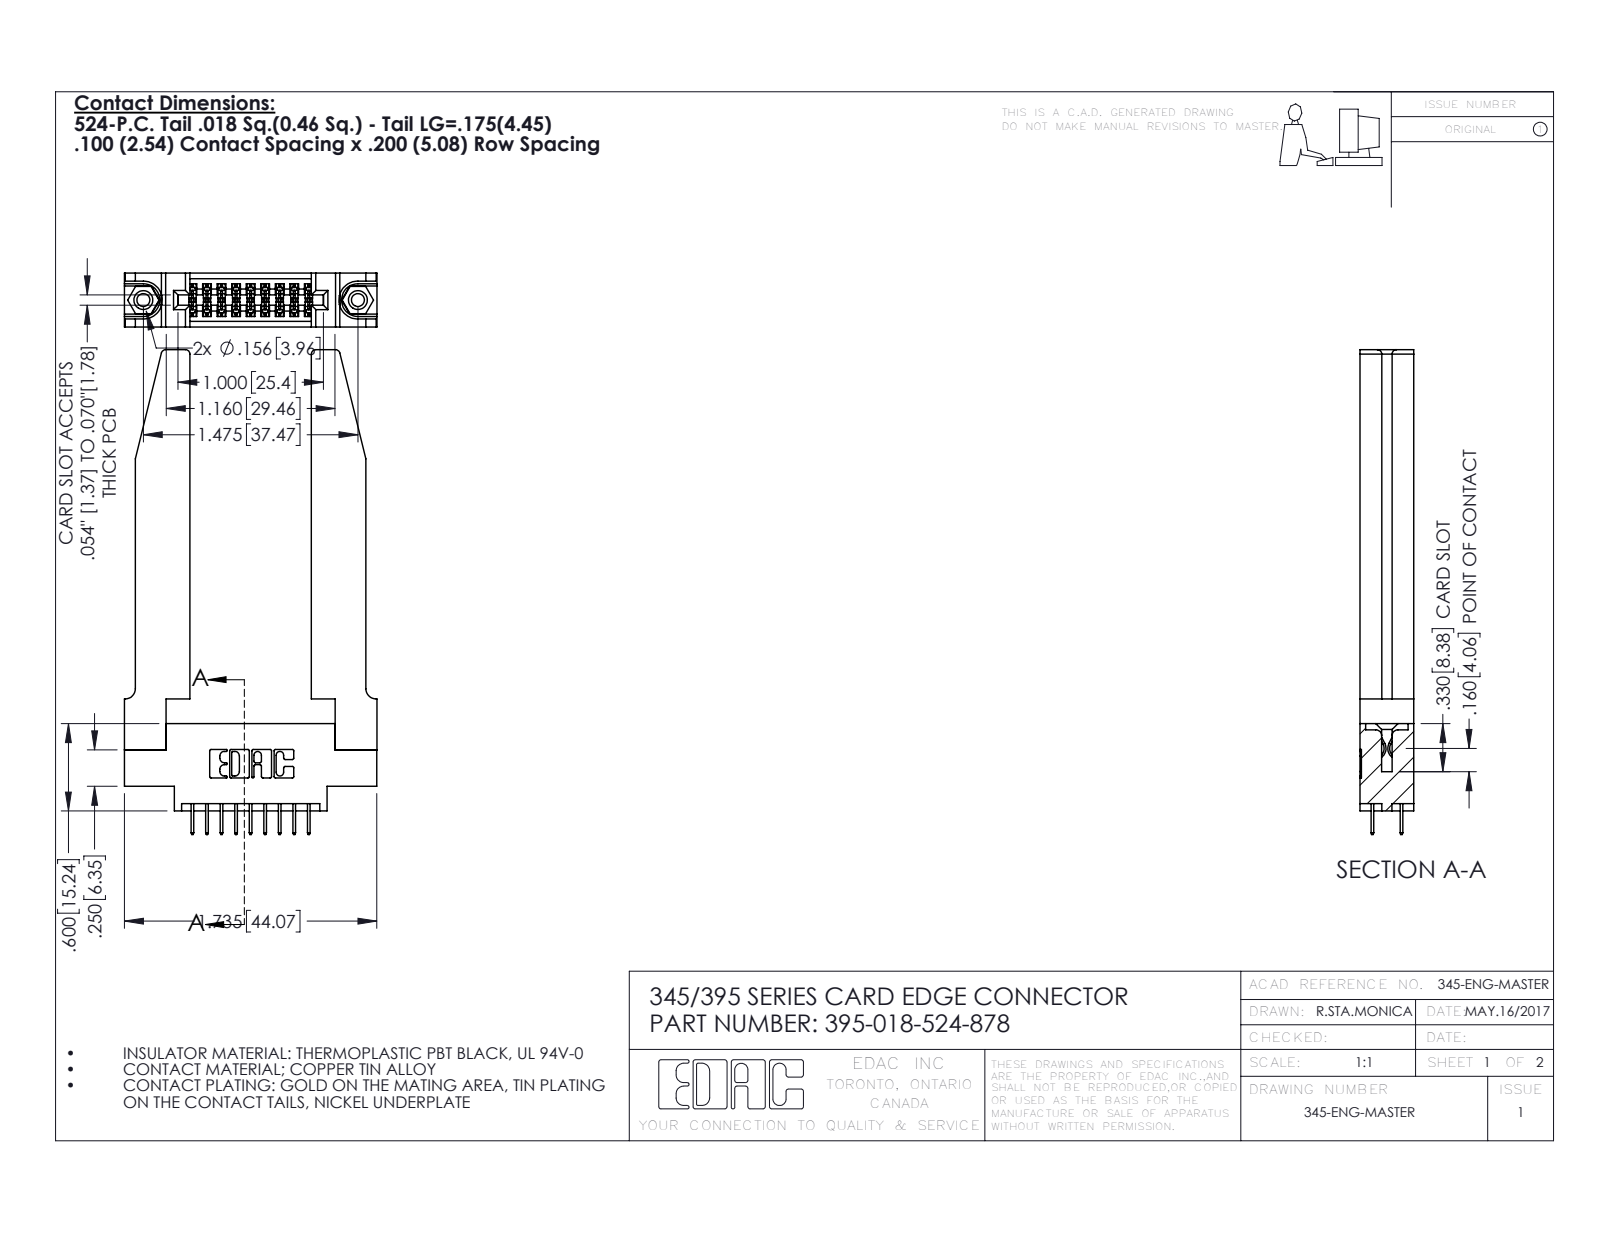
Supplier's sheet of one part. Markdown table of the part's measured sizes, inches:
| quantity | value |
| --- | --- |
| part name | 345-220-078_345-220-078; 345 Part_0.170 Offset - 0.156 Dia-TH; 345-250-001_345-250-001-102; 345-292-001_345-293-124 (+1 more) |
| STEP written by | SolidWorks 2016 (CONFIG_CONTROL_DESIGN) |
| units | inches |
| bodies | 23 solids, 1336 faces (928 planar, 356 cylindrical, 52 other) |
| overall size | 3.332 × 1.736 × 0.37 |
| volume | 0.708 in³ |
| surface area | 18.51 in² |
| round holes (diameter × count) | 0.089 × 2, 0.125 × 2, 0.156 × 2, 0.064 × 1 |
| round bosses / shafts (diameter × count) | 0.155 × 2 |
| partial cylindrical surfaces (radius × count) | 0.006 × 27, 0.01 × 22, 0.03 × 8, 0.007 × 6, 0.031 × 6, 0.026 × 3, 0.014 × 2, 0.019 × 2 |
| main face-to-face distances | 0.37, 0.072, 0.298, 0.148, 0.15, 0.22, 0.077, 0.835, 0.095, 0.071 |
| hole center spacings | 0.27, 1.244, 1.475 |
